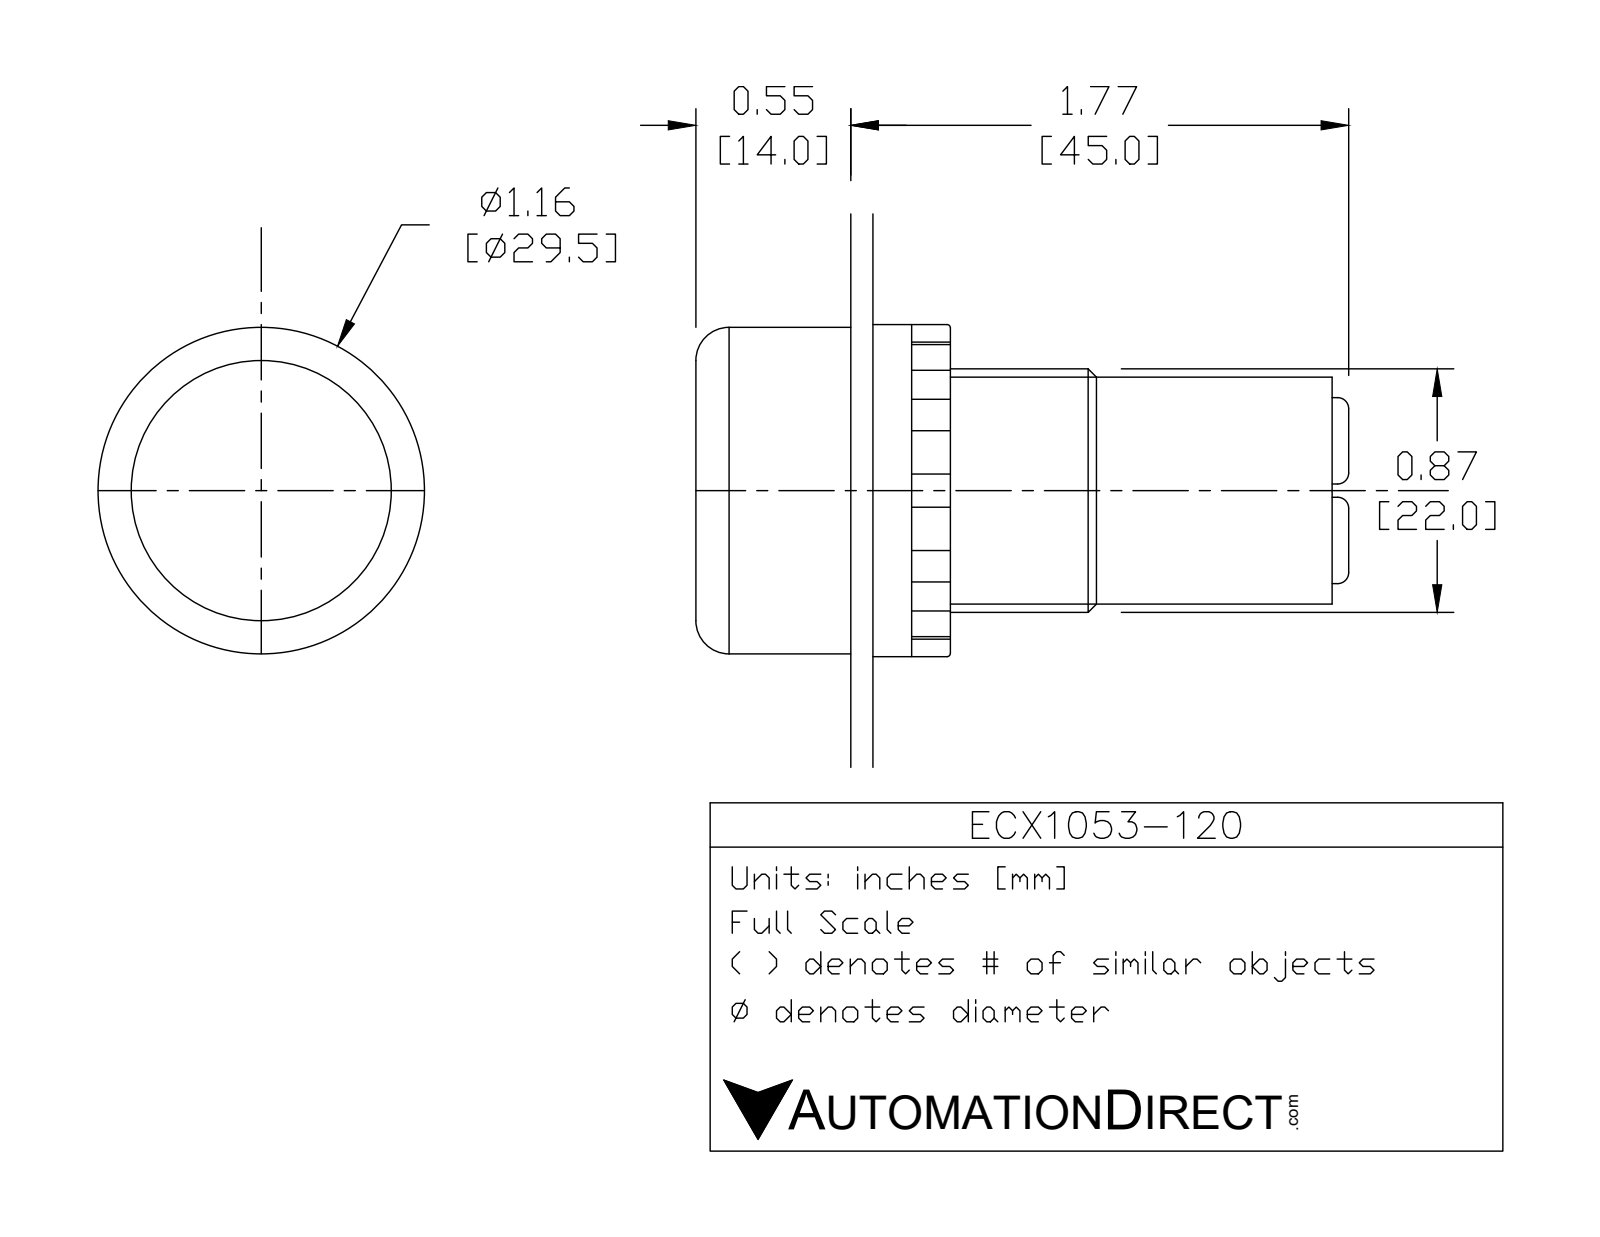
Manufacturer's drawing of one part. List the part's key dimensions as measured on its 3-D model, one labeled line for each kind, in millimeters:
Part name (STEP PRODUCT): ECX1053-120
STEP written by: SolidWorks 2017 (AUTOMOTIVE_DESIGN)
Units: millimetres
Bodies: 6 solids, 125 faces (63 planar, 41 cylindrical, 21 other)
Overall size (bounding box): 59 × 30 × 30
Volume: 26 294 mm³ · Surface area: 9 700 mm²
Round holes (diameter × count): ⌀5.5 ×2, ⌀22.5 ×1
Round bosses / shafts (diameter × count): ⌀4 ×2, ⌀30 ×1, ⌀29 ×1, ⌀26.5 ×1, ⌀22 ×1, ⌀20 ×1
Partial cylindrical surfaces — rounded edges, fillets, slot ends (radius × count): R1 ×12, R9 ×1
Main face-to-face distances: 13.5, 0.5, 14, 20, 6, 6.5, 39, 7, 13, 27
Hole centre spacings: 4.62, 9.24
